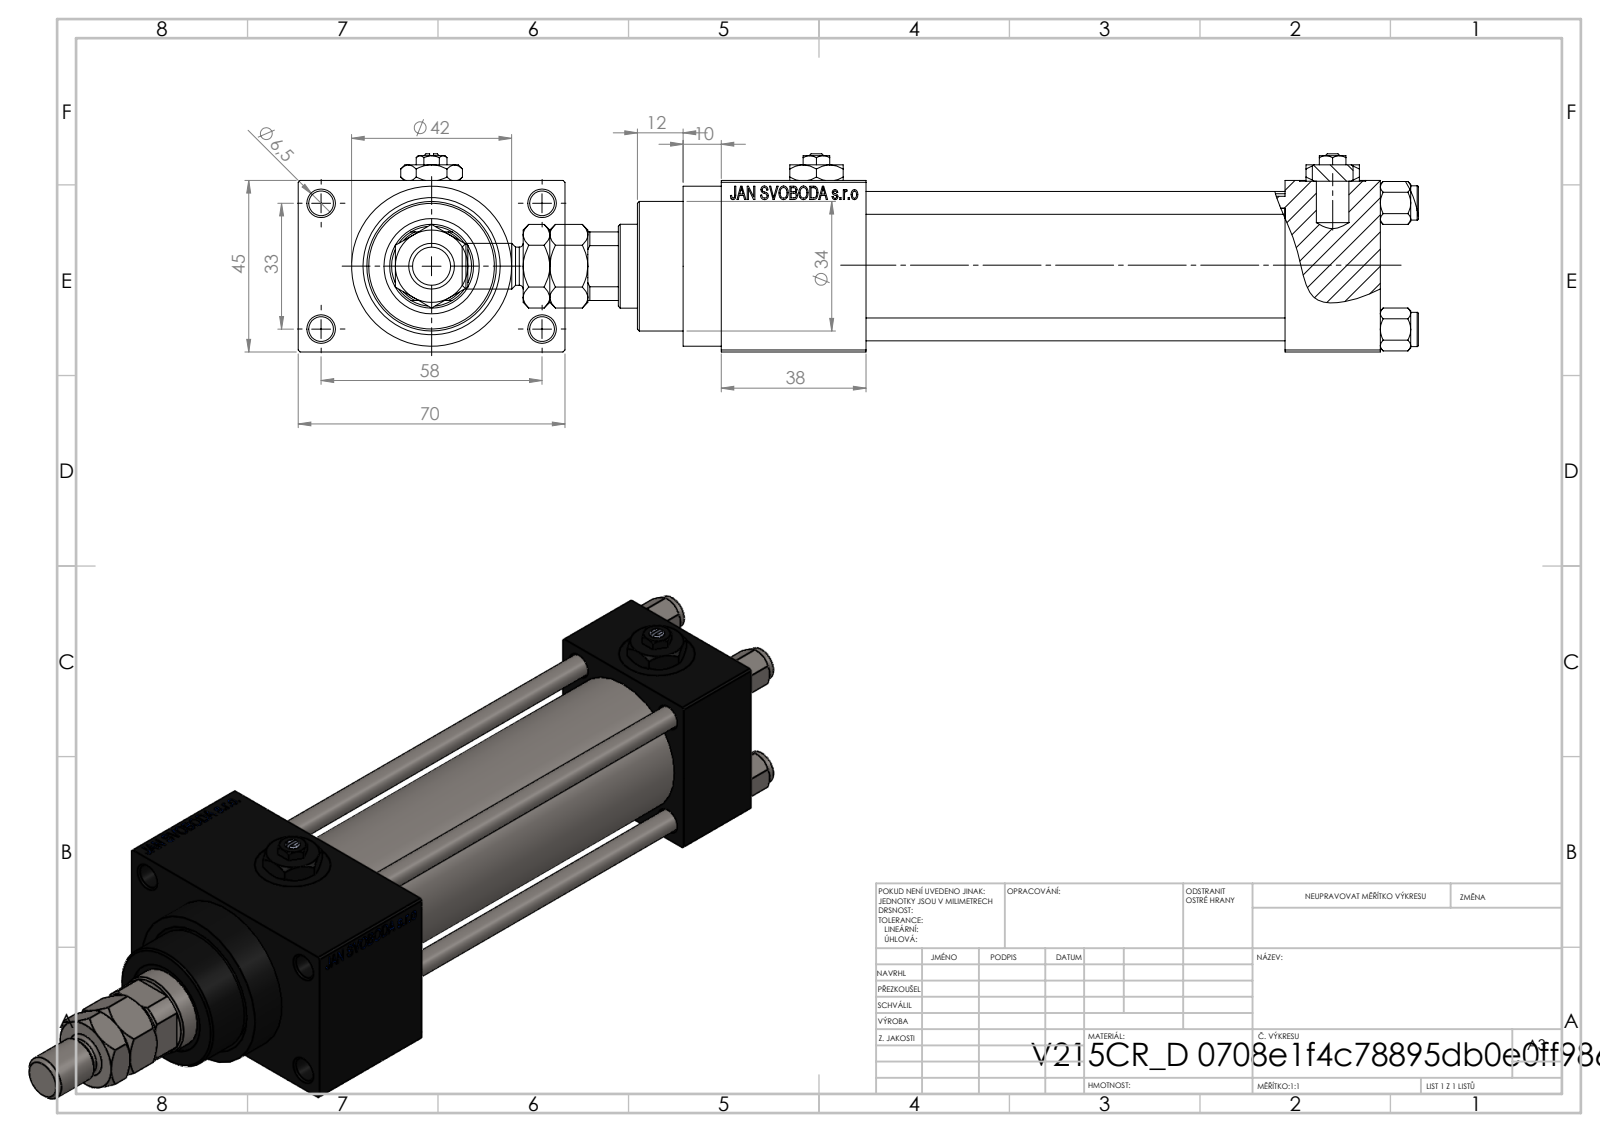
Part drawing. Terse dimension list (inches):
name: V215CR_D_Body; V215_VC_A; V215CR_D_TYCINKA; NUT_M5_D (+3 more)
written by: SolidWorks 2019 (CONFIG_CONTROL_DESIGN)
unit: in
bodies: 14 solids, 1253 faces (557 planar, 104 cylindrical, 592 other)
size: 9.882 × 2.756 × 2.047
volume: 18.28 in³; area: 163.2 in²
holes: 4× ⌀0.236, 4× ⌀0.256, 2× ⌀0.276, 2× ⌀0.518, 2× ⌀0.787, 1× ⌀0.413, 1× ⌀0.866, 1× ⌀0.945, 1× ⌀0.984, 1× ⌀1.26, 1× ⌀1.299
bosses: 4× ⌀0.354, 1× ⌀1.654, 1× ⌀1.496, 1× ⌀1.339, 1× ⌀0.472, 1× ⌀0.394
rounds: 1× R0.413
face distances: 1.772, 0.984, 0.492, 2.264, 4.331, 5.315, 5.827, 2.756, 1.496, 6.811
hole spacings: 0.488, 0.924, 1.307, 1.314, 1.392, 1.795, 2.219, 1.299
